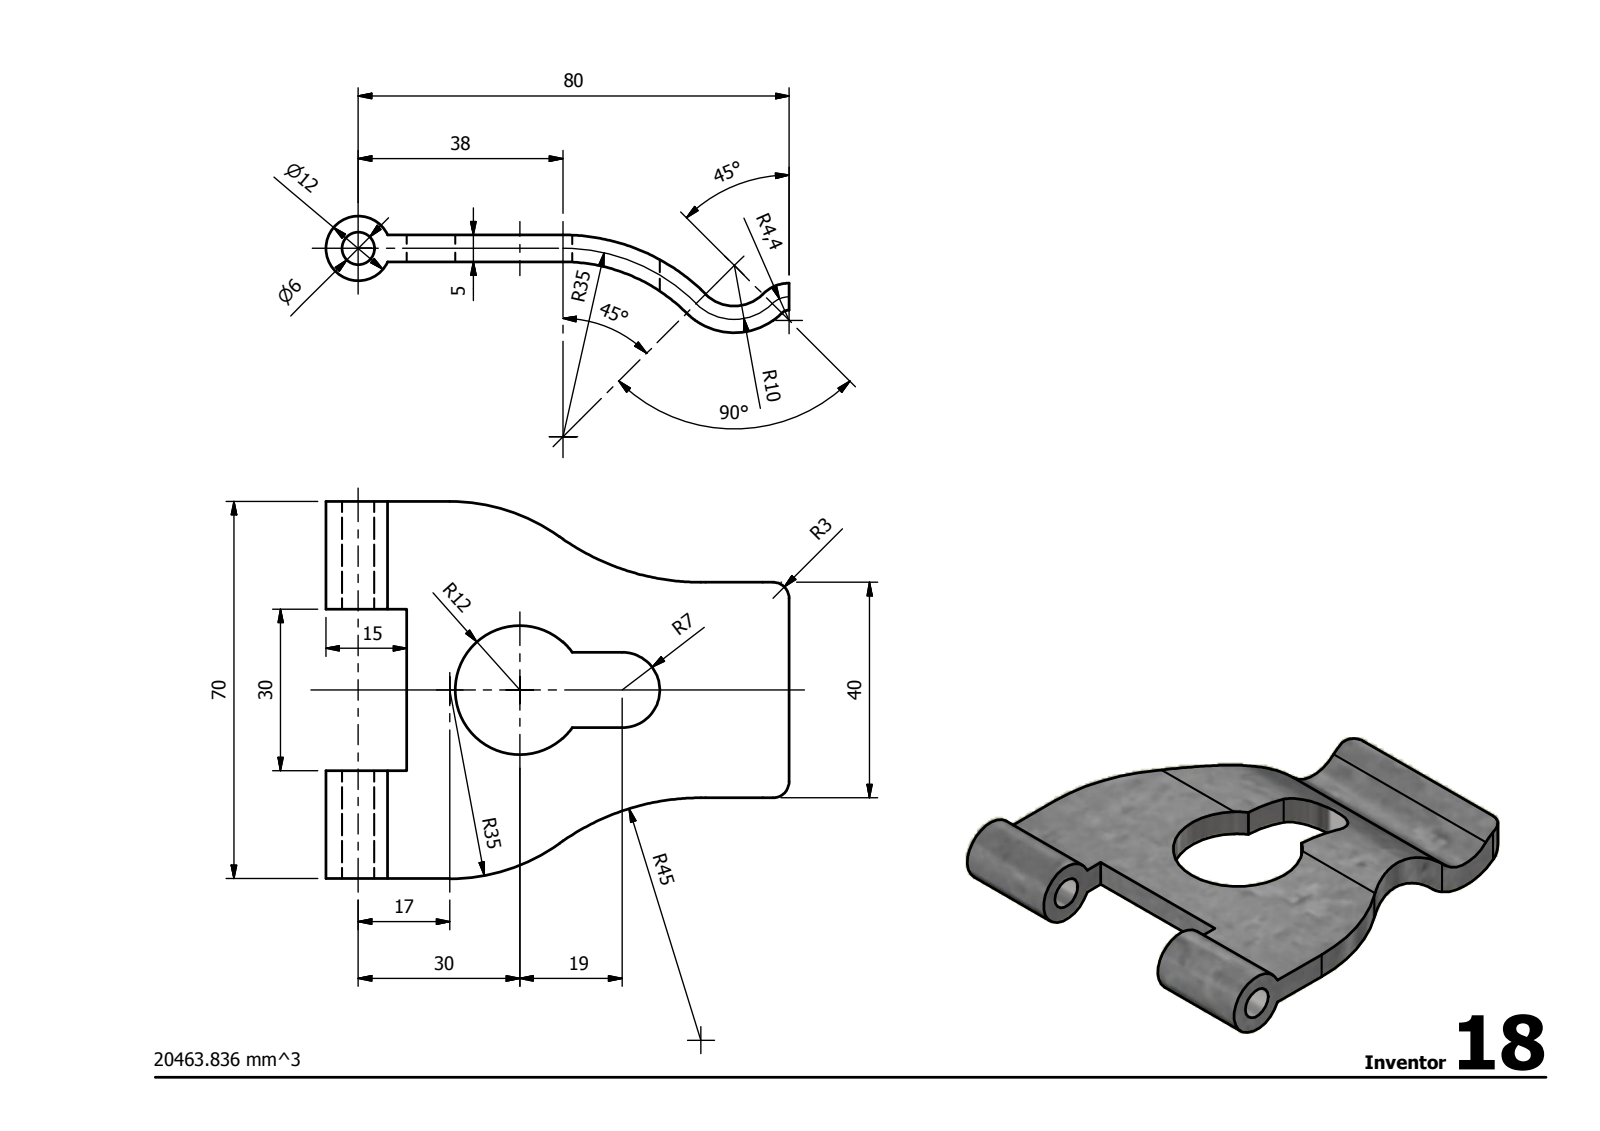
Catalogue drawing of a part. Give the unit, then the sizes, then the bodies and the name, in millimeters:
Units: millimetres
Overall size (bounding box): 86 × 70 × 21.68
Round holes (diameter × count): ⌀6 ×1, ⌀24 ×1
Round bosses / shafts (diameter × count): ⌀12 ×1
Partial cylindrical surfaces — rounded edges, fillets, slot ends (radius × count): R3 ×2, R45 ×2, R1.9 ×1, R6.9 ×1, R7 ×1, R7.5 ×1, R12.5 ×1, R32.5 ×1
Main face-to-face distances: 5, 20, 50, 71, 15, 55, 35, 70, 30, 28
Volume: 20 462 mm³ · Surface area: 10 961 mm²
Bodies: 1 solid, 30 faces (12 planar, 18 cylindrical, 0 other)
STEP written by: Autodesk Inventor 2014 (AUTOMOTIVE_DESIGN)
